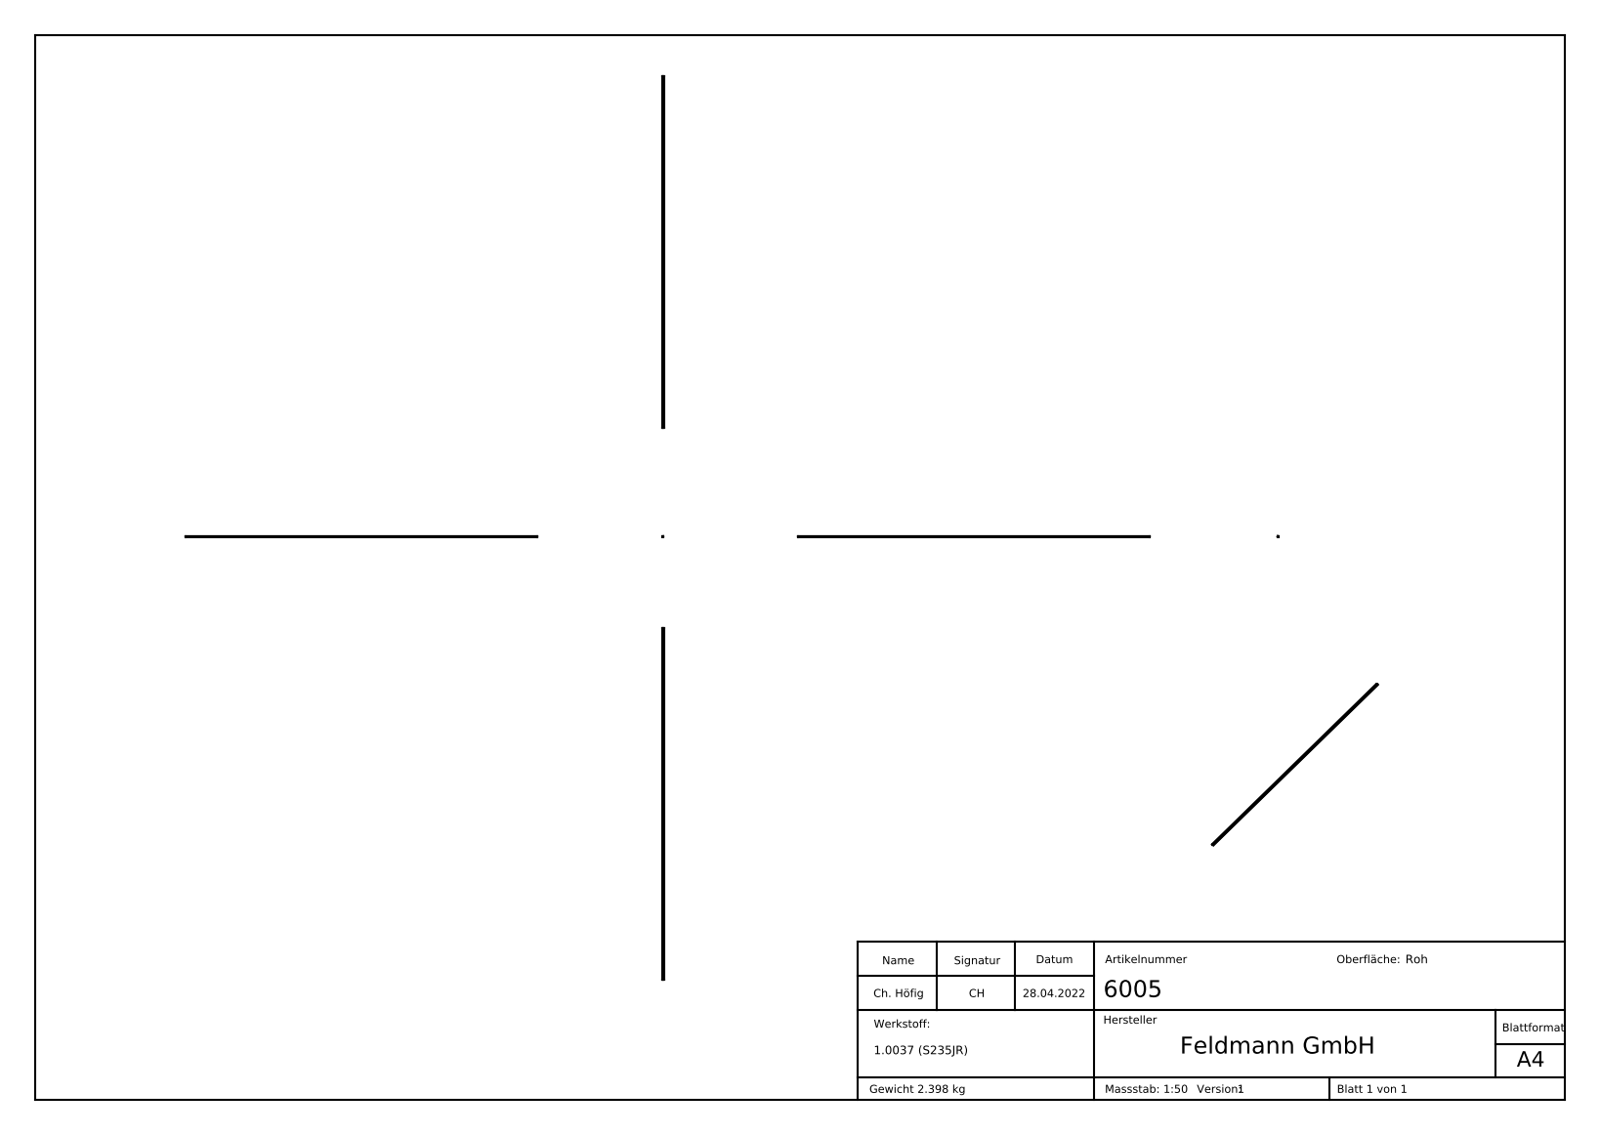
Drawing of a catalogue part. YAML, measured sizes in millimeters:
part_name: "6005"
step_written_by: "SolidWorks 2018 (CONFIG_CONTROL_DESIGN)"
units: millimeters
bodies: {solids: 1, faces: 217, planar: 108, cylindrical: 6, other: 103}
overall_size: [3300, 16, 8]
volume: 307443
surface_area: 169764
partial_cylinders:
  - {radius: 13, count: 4}
  - {radius: 3, count: 2}
face_to_face_distances: [8, 3300, 0.5, 3299.5, 0.73, 1.78, 1.21, 0.83, 1.57, 0.81]
